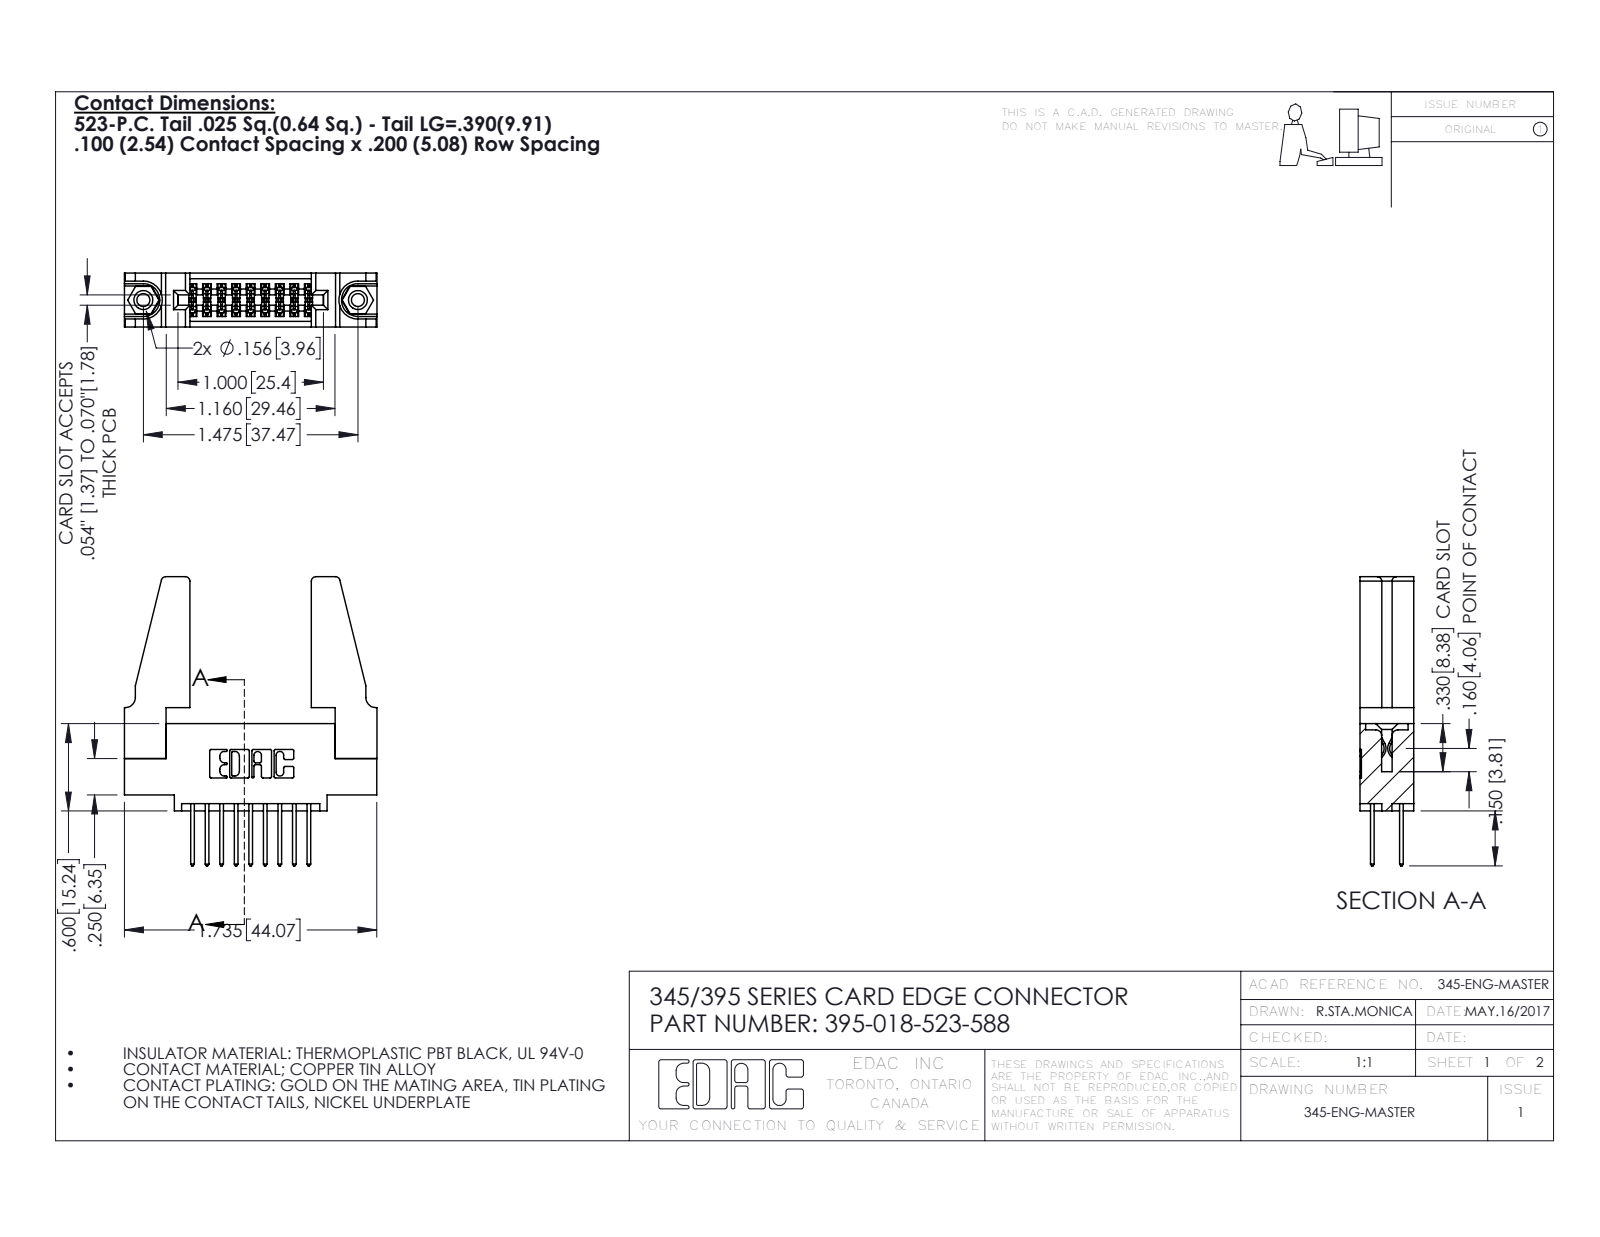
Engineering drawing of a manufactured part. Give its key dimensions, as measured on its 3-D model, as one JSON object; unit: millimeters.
{"part_name": "345-292-001_345-293-123; 345-220-078_345-220-088; 395-018-523-588; 345-250-001_345-250-001-102 (+1 more)", "step_written_by": "SolidWorks 2016 (CONFIG_CONTROL_DESIGN)", "units": "millimeters", "bodies": {"solids": 23, "faces": 1154, "planar": 750, "cylindrical": 388, "other": 16}, "overall_size": [50.5, 44.1, 9.4], "volume_mm3": 7190, "surface_area_mm2": 8568, "round_holes": [[2.3, 2], [3.2, 2], [4, 2], [1.6, 1]], "round_bosses_or_shafts": [[3.9, 2]], "partial_cylinders_radius": [[0.2, 27], [0.3, 22], [0.3, 18], [0.8, 8], [0.2, 6], [0.8, 6], [0.7, 3], [0.4, 2]], "face_to_face_distances": [9.4, 1.8, 7.6, 5.1, 2.5, 6.9, 0.6, 5.7, 3.8, 3.8], "hole_center_spacings": [6.9, 31.6, 37.5]}
